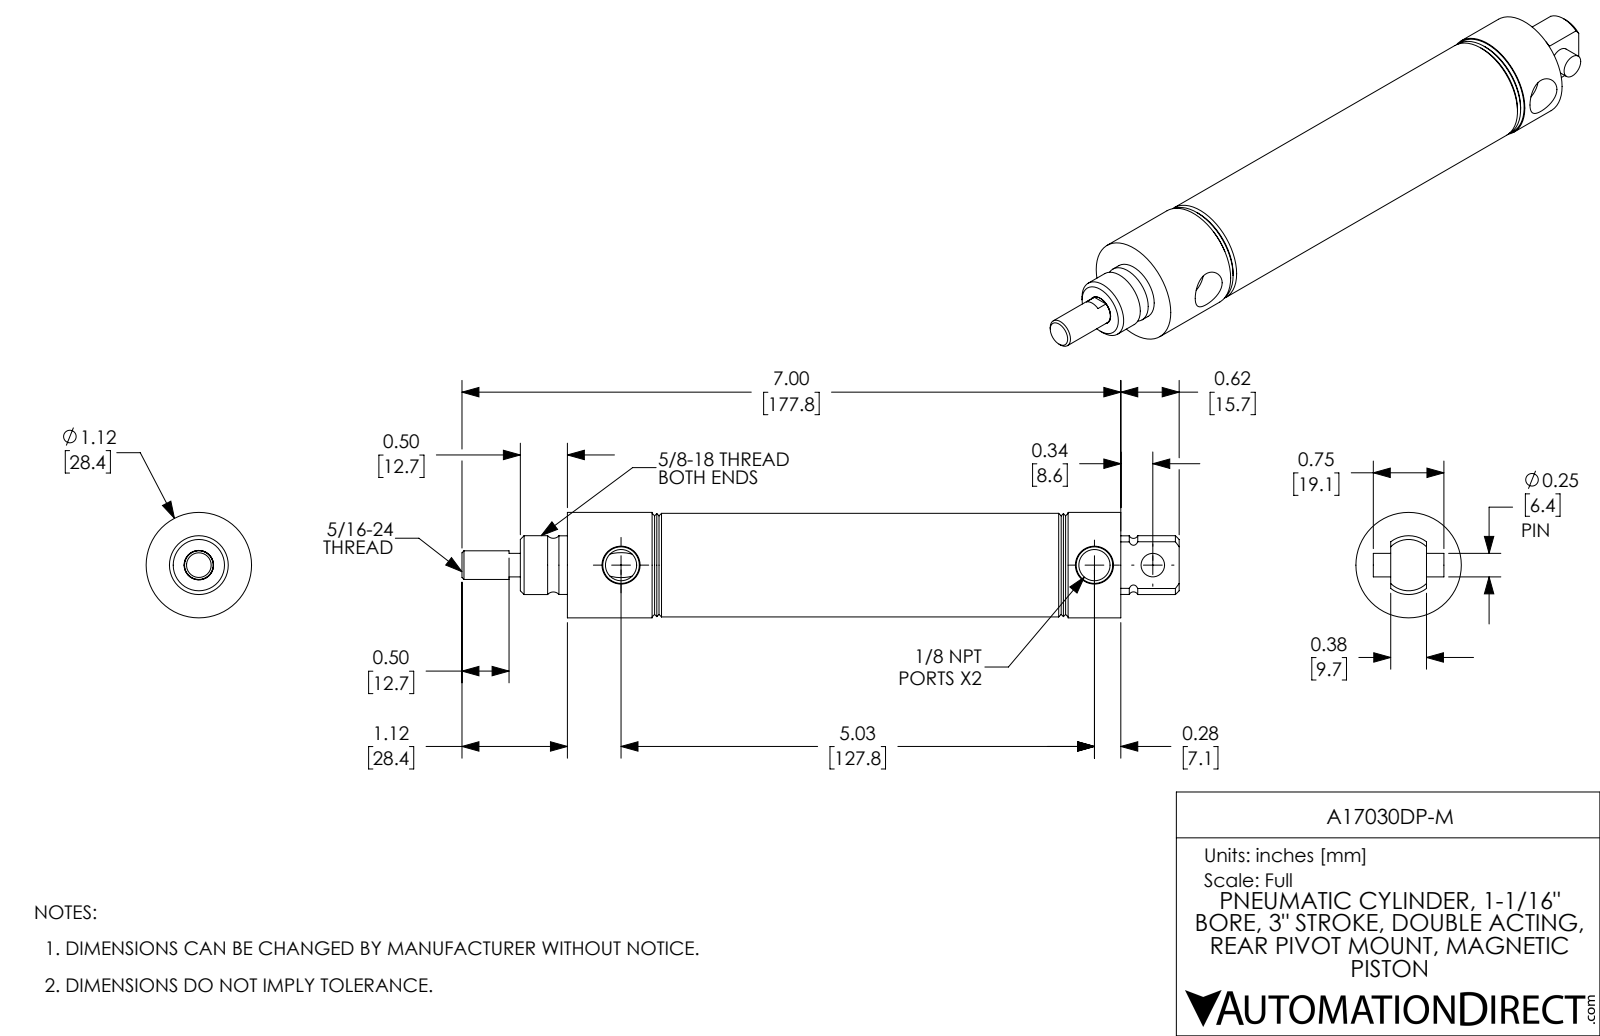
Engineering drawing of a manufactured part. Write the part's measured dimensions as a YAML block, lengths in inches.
part_name: "A17030DP-M; A17030DP-M-PIN; A17030DP-M-Rod; A17030DP-M-MainBody"
step_written_by: "SolidWorks 2017 (AUTOMOTIVE_DESIGN)"
units: inches
bodies: {solids: 3, faces: 92, planar: 22, cylindrical: 32, other: 38}
overall_size: [7.62, 1.12, 1.12]
volume: 3.446
surface_area: 50.08
round_holes:
  - {diameter: 0.332, count: 2}
  - {diameter: 0.25, count: 1}
  - {diameter: 0.312, count: 1}
  - {diameter: 1.063, count: 1}
round_bosses_or_shafts:
  - {diameter: 1.12, count: 1}
  - {diameter: 1.1, count: 1}
  - {diameter: 0.625, count: 1}
  - {diameter: 0.623, count: 1}
  - {diameter: 0.304, count: 1}
partial_cylinders:
  - {radius: 0.313, count: 1}
face_to_face_distances: [0.5, 4.69, 3.5, 3, 1.19, 1.69, 4.69, 5.88, 4.19, 1.19]
hole_center_spacings: [0.62, 5.03, 5.65]
